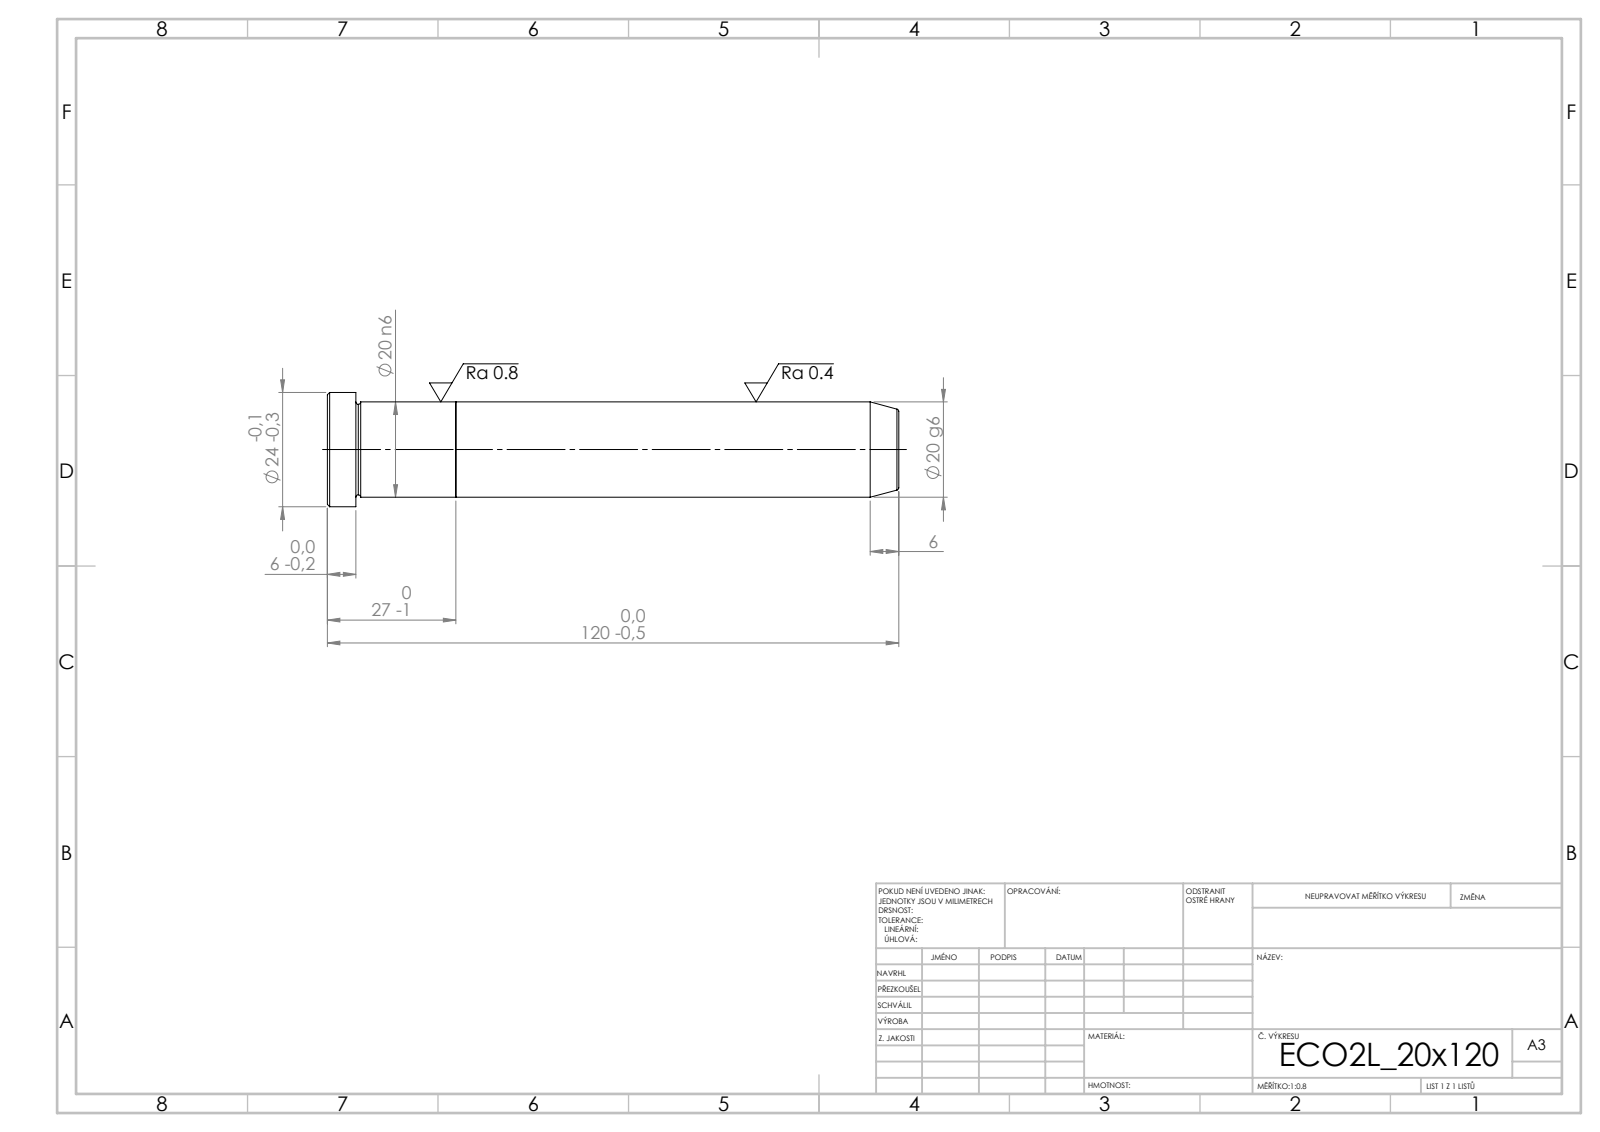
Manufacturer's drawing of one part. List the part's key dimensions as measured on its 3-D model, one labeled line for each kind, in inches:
STEP written by: SolidWorks 2019 (CONFIG_CONTROL_DESIGN)
Units: inches
Bodies: 2 solids, 21 faces (5 planar, 6 cylindrical, 10 other)
Overall size (bounding box): 4.724 × 0.945 × 0.945
Volume: 2.332 in³ · Surface area: 14.02 in²
Round bosses / shafts (diameter × count): ⌀0.945 ×1, ⌀0.787 ×1
Main face-to-face distances: 1.063, 3.661, 4.724, 4.488, 0.827, 0.236
